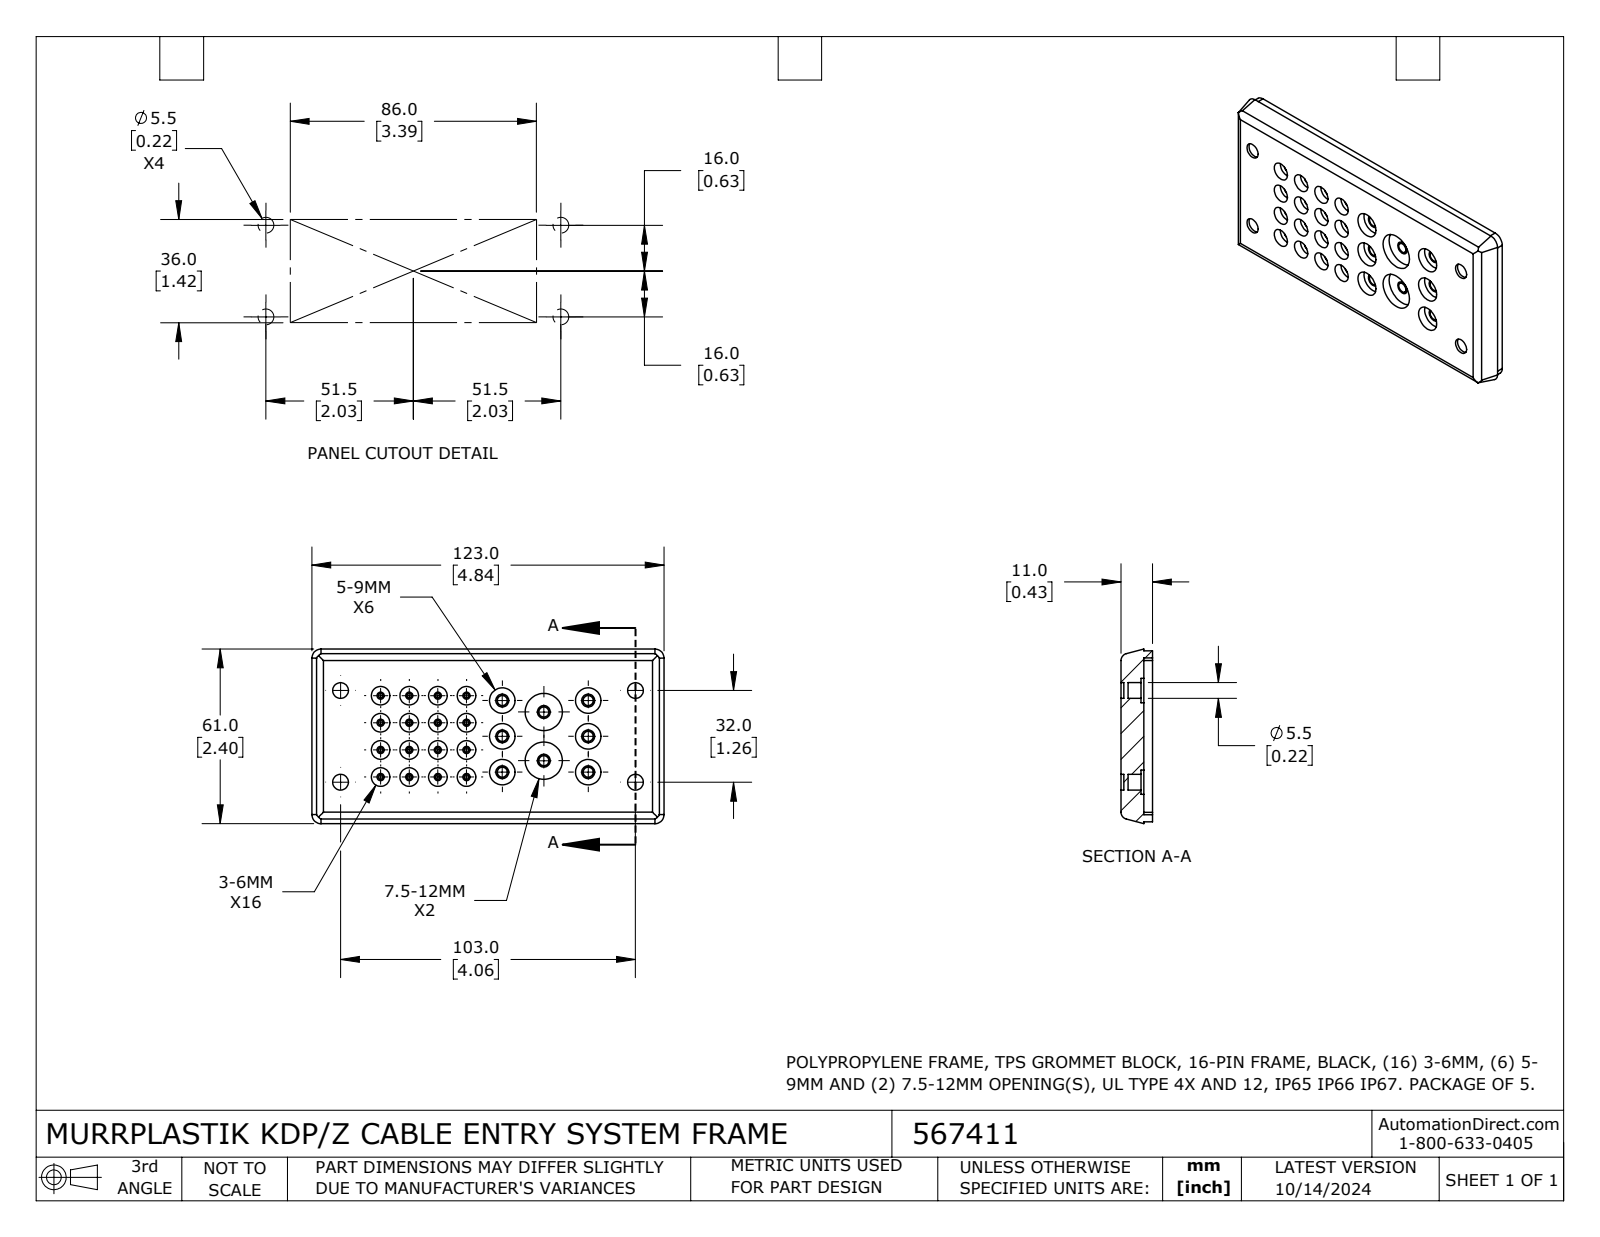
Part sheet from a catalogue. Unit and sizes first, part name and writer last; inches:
Units: inches
Overall size (bounding box): 4.843 × 2.402 × 0.433
Round holes (diameter × count): ⌀0.098 ×16, ⌀0.256 ×16, ⌀0.177 ×8, ⌀0.35 ×6, ⌀0.217 ×4, ⌀0.335 ×4, ⌀0.512 ×2
Round bosses / shafts (diameter × count): ⌀0.059 ×16, ⌀0.138 ×8
Partial cylindrical surfaces — rounded edges, fillets, slot ends (radius × count): R0.012 ×8, R0.035 ×4, R0.098 ×4, R0.138 ×4, R0.244 ×4, R0.266 ×4
Main face-to-face distances: 0.217, 0.098, 0.315, 0.118, 0.197, 0.096, 0.433, 0.283, 1.874, 0.38
Hole centre spacings: 0.394, 0.542, 0.844, 0.372, 0.746, 0.787, 0.871, 1.085
Volume: 2.701 in³ · Surface area: 37.43 in²
Bodies: 1 solid, 316 faces (114 planar, 198 cylindrical, 4 other)
Part name (STEP PRODUCT): 567411
STEP written by: SolidWorks 2023 (CONFIG_CONTROL_DESIGN)
